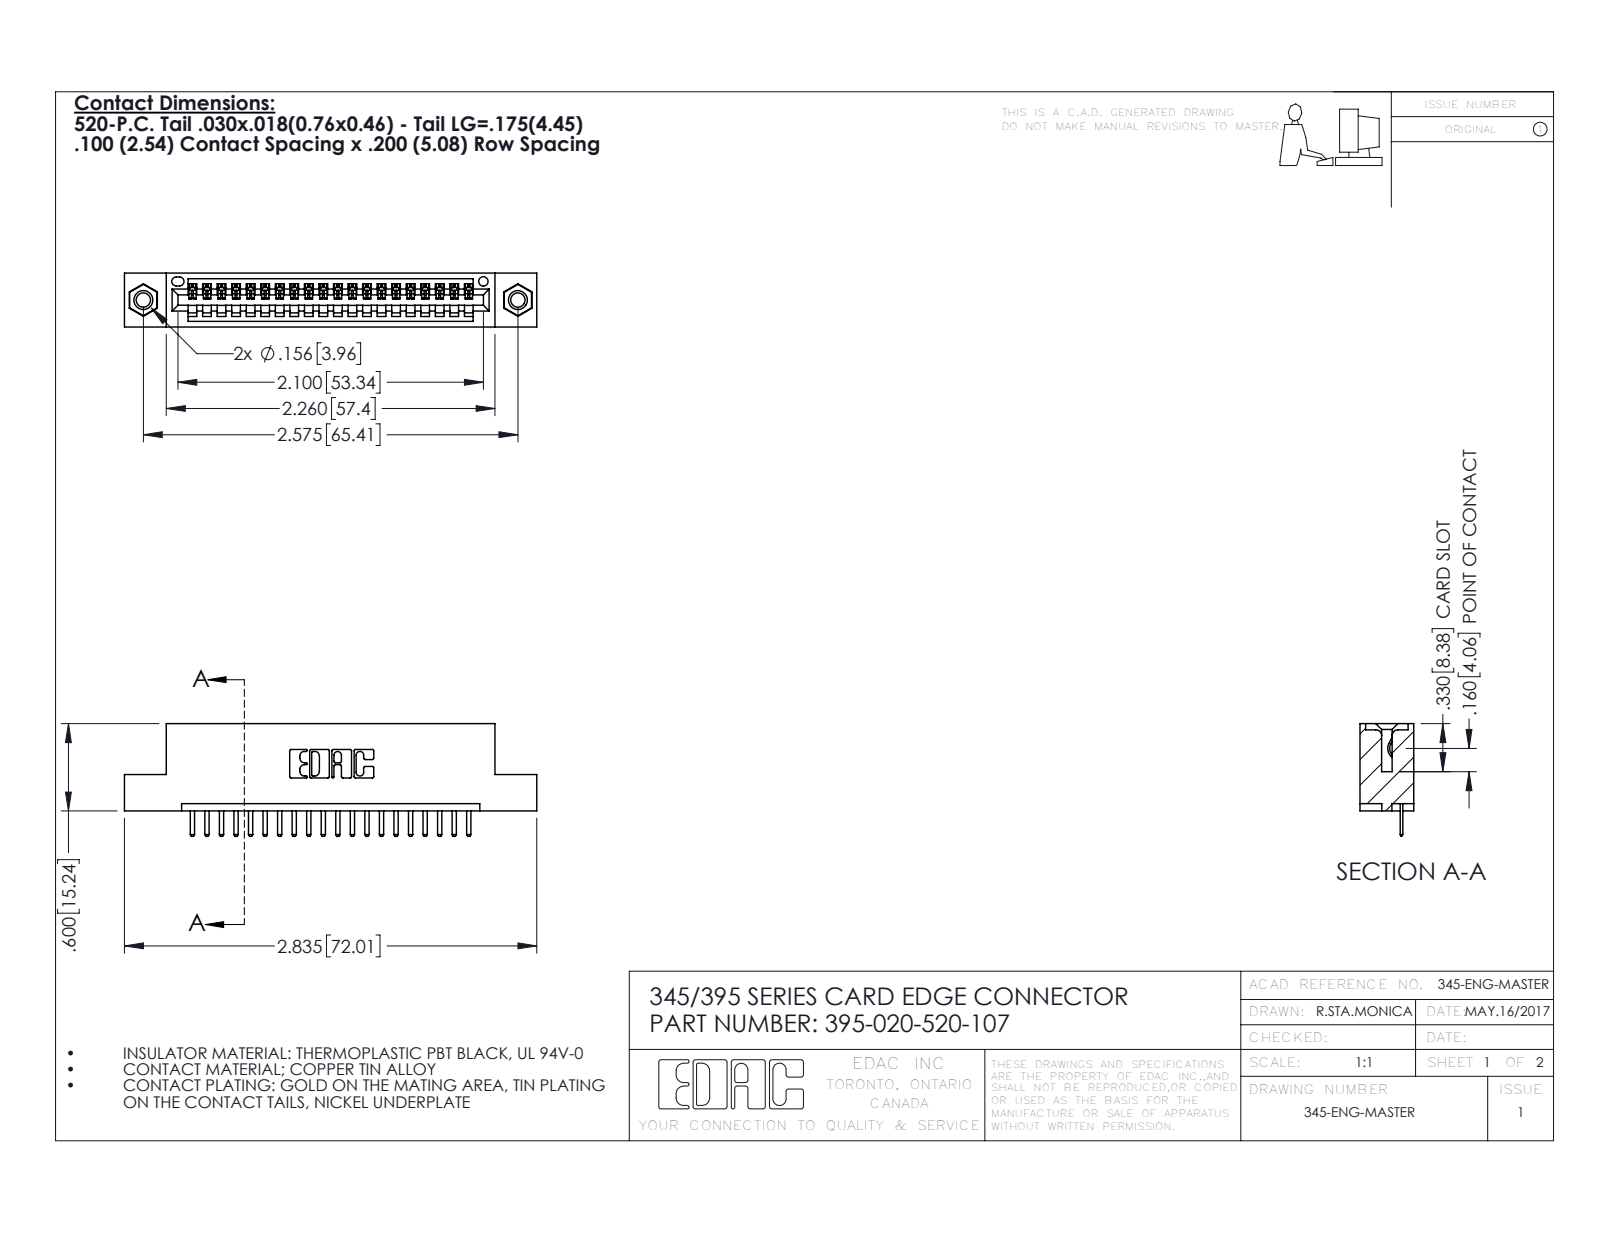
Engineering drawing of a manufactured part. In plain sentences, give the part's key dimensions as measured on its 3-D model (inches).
The part is named "345-250-001_345-250-005-103; 345 Part_Flush Mounting Lugs - 0.156 Dia-TI; 345-292-001_345-293-120; 395-020-520-107". Its 3-D file was written by "SolidWorks 2016 (CONFIG_CONTROL_DESIGN)". It is 23 solids with 1426 faces: 952 planar, 458 cylindrical and 16 other. Overall it measures 2.835 by 0.775 by 0.37 inches. Its volume is 0.402 cubic inches and its surface area 12.87 square inches. Round holes: 2 of diameter 0.098, 2 of diameter 0.125, 2 of diameter 0.156, 1 of diameter 0.064. Round bosses or shafts: 2 of diameter 0.155. Partial cylindrical surfaces (rounded edges, fillets, slot ends): 42 of radius 0.01, 40 of radius 0.006, 22 of radius 0.01, 6 of radius 0.007, 6 of radius 0.031, 3 of radius 0.026, 2 of radius 0.031, 2 of radius 0.04. The main face-to-face distances are 0.072, 0.298, 0.37, 0.2, 0.098, 0.272, 0.025, 0.225, 0.072, 0.149. The hole center spacings are 0.27, 2.341, 2.575.
